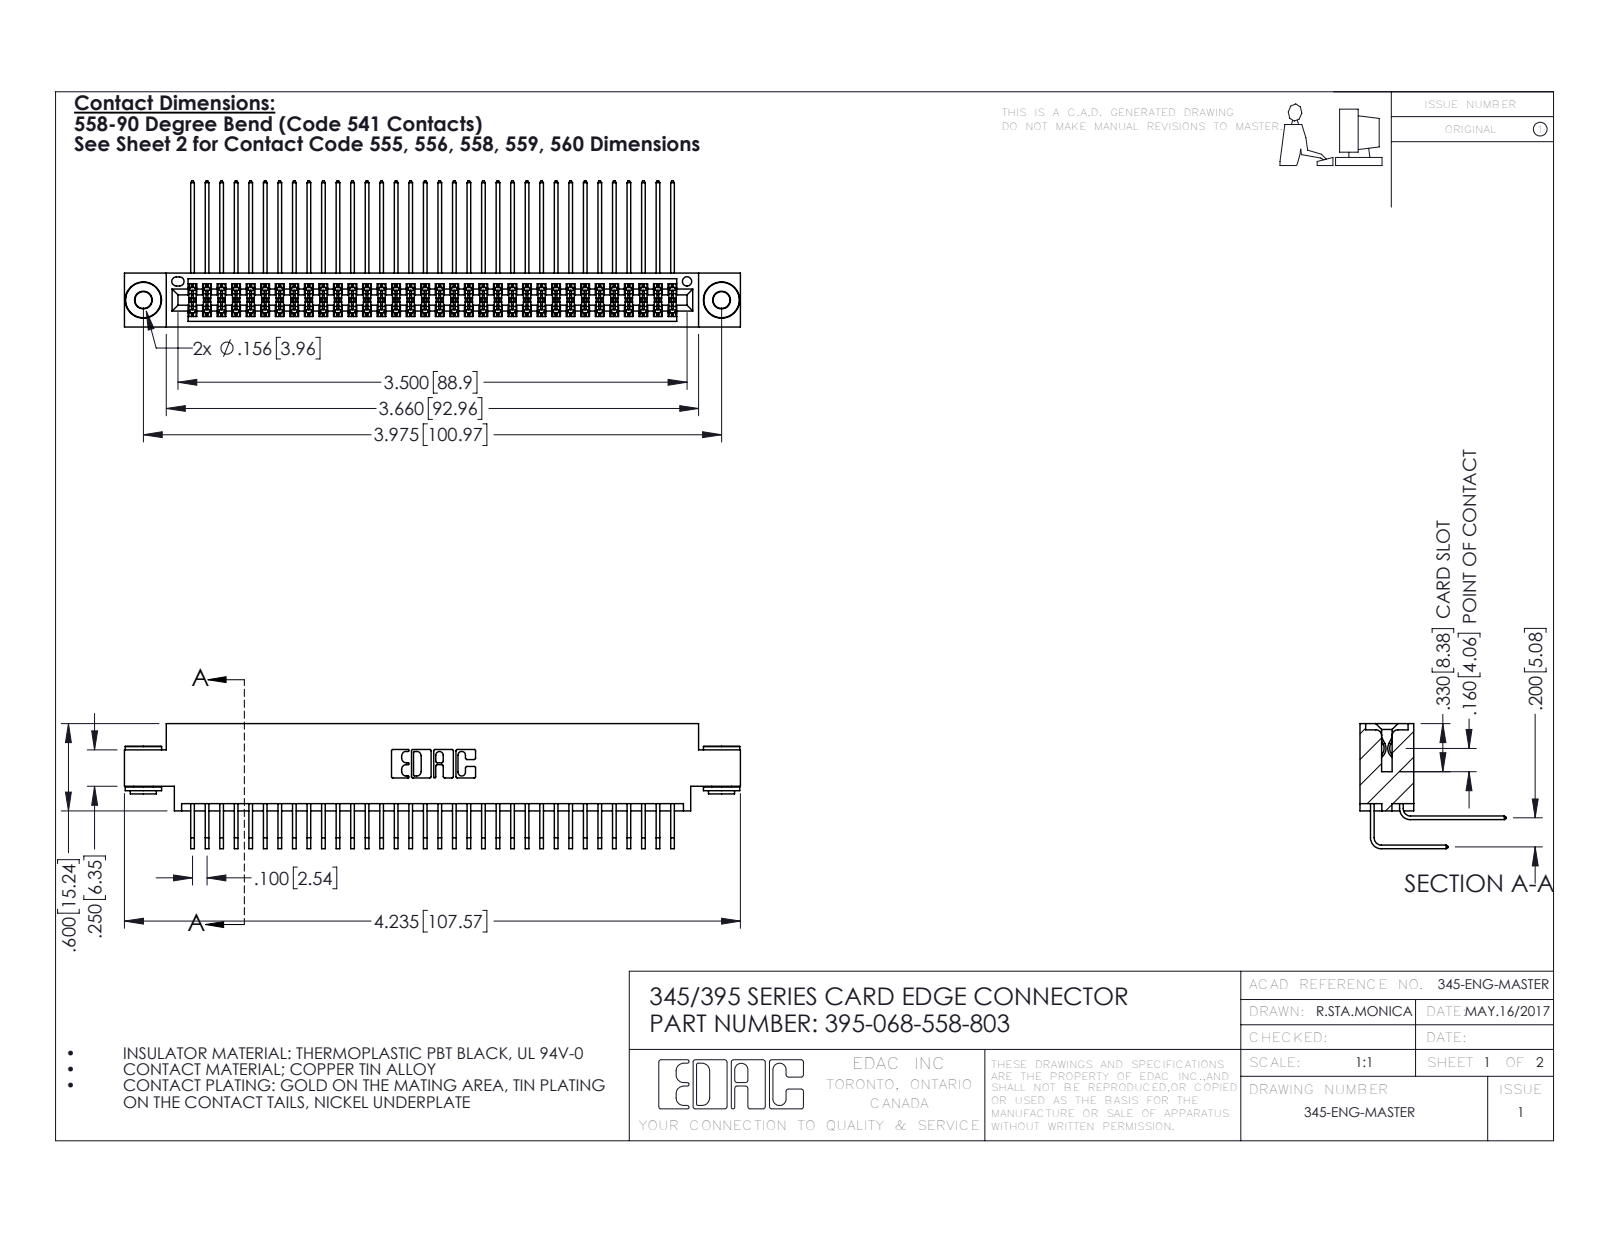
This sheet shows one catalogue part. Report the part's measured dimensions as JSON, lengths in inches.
{"part_name": "345-250-002_345-250-002-102; 395-068-558-803; 345-292-001_558 559 Tail - 1; 345-292-001_558 Tail - 2 (+1 more)", "step_written_by": "SolidWorks 2016 (CONFIG_CONTROL_DESIGN)", "units": "inches", "bodies": {"solids": 71, "faces": 3704, "planar": 2474, "cylindrical": 1222, "other": 8}, "overall_size": [4.235, 1.005, 0.859], "volume_in3": 0.651, "surface_area_in2": 27.61, "round_holes": [[0.116, 2], [0.156, 2], [0.064, 1]], "round_bosses_or_shafts": [[0.25, 2], [0.18, 2], [0.136, 2]], "partial_cylinders_radius": [[0.006, 103], [0.01, 22], [0.007, 6], [0.031, 6], [0.026, 3], [0.014, 2], [0.019, 2], [0.022, 2]], "face_to_face_distances": [0.072, 0.298, 0.2, 0.37, 0.098, 0.272, 0.025, 0.225, 0.175, 0.025], "hole_center_spacings": [0.27, 3.74, 3.975]}
